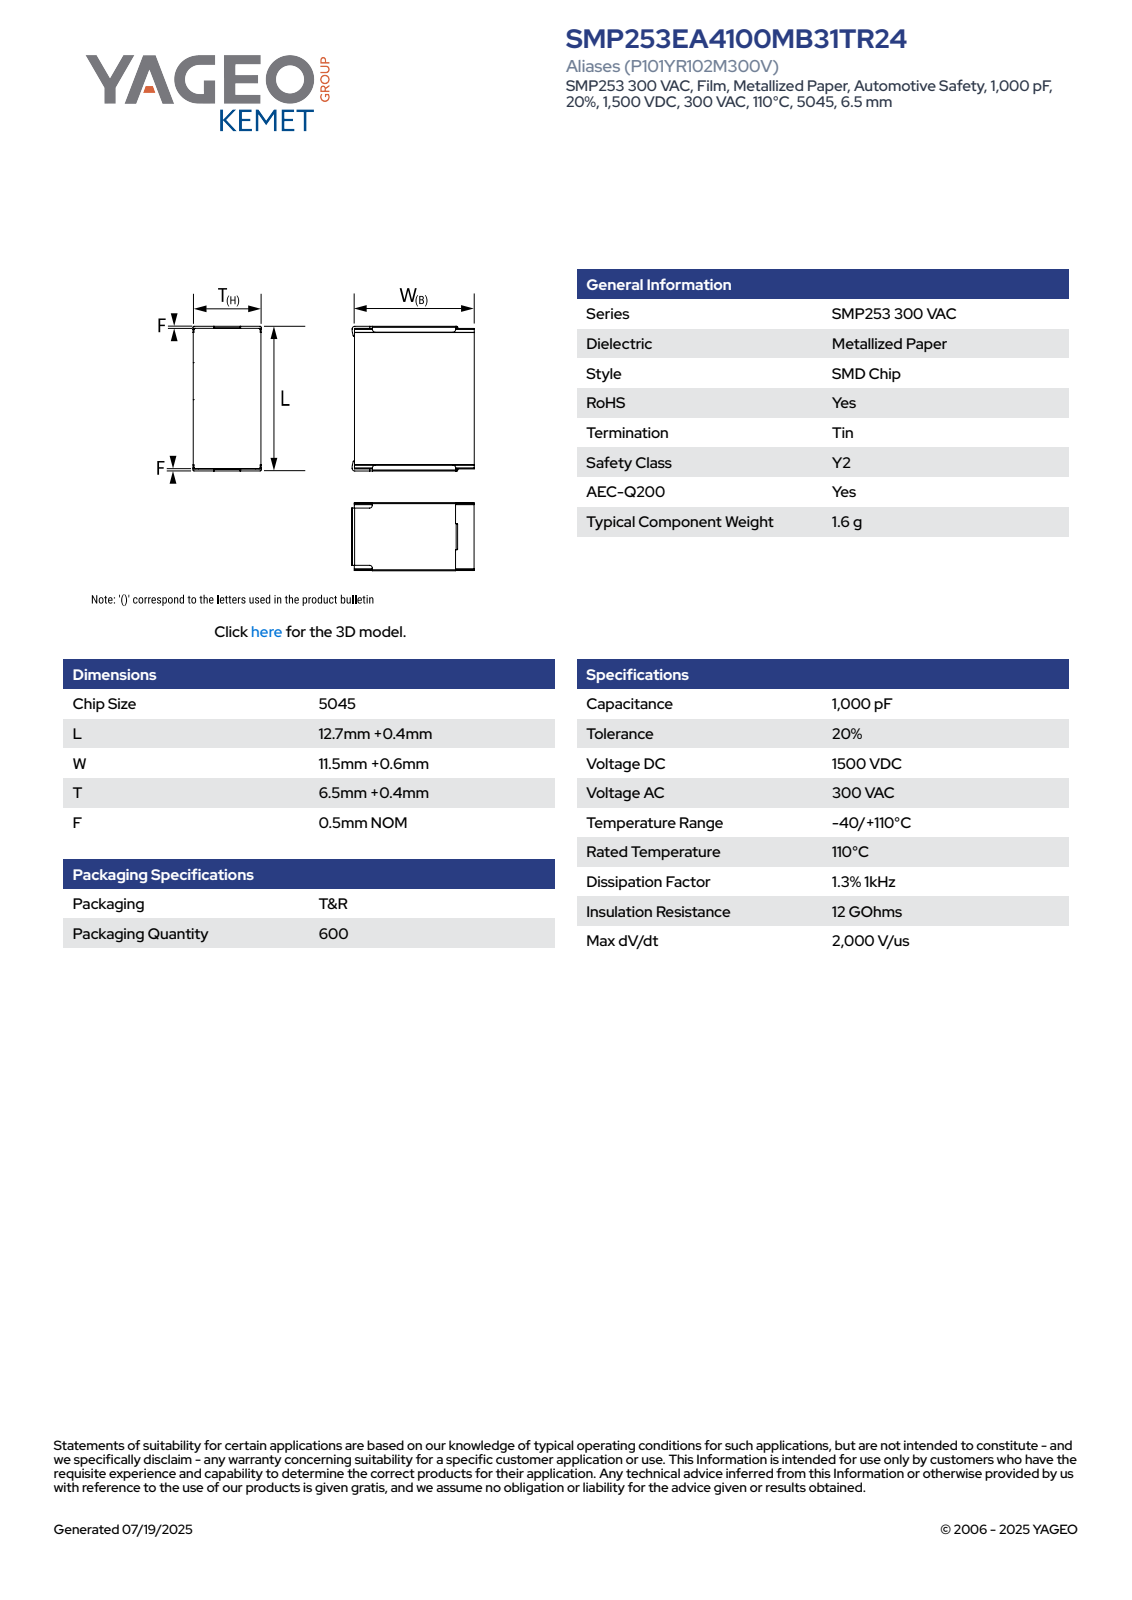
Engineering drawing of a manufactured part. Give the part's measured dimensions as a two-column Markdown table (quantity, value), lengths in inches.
| quantity | value |
| --- | --- |
| part name | CFS_KSTD_5045_L13.1W12.1T6.9F0.5 |
| STEP written by | SolidWorks 2021 (AUTOMOTIVE_DESIGN) |
| units | inches |
| bodies | 4 solids, 117 faces (103 planar, 14 cylindrical, 0 other) |
| overall size | 0.516 × 0.493 × 0.285 |
| volume | 0.065 in³ |
| surface area | 1.09 in² |
| partial cylindrical surfaces (radius × count) | 0.016 × 10, 0.018 × 4 |
| main face-to-face distances | 0.272, 0.457, 0.516, 0.02, 0.496, 0.279, 0.476, 0.019, 0.286, 0.492 |
